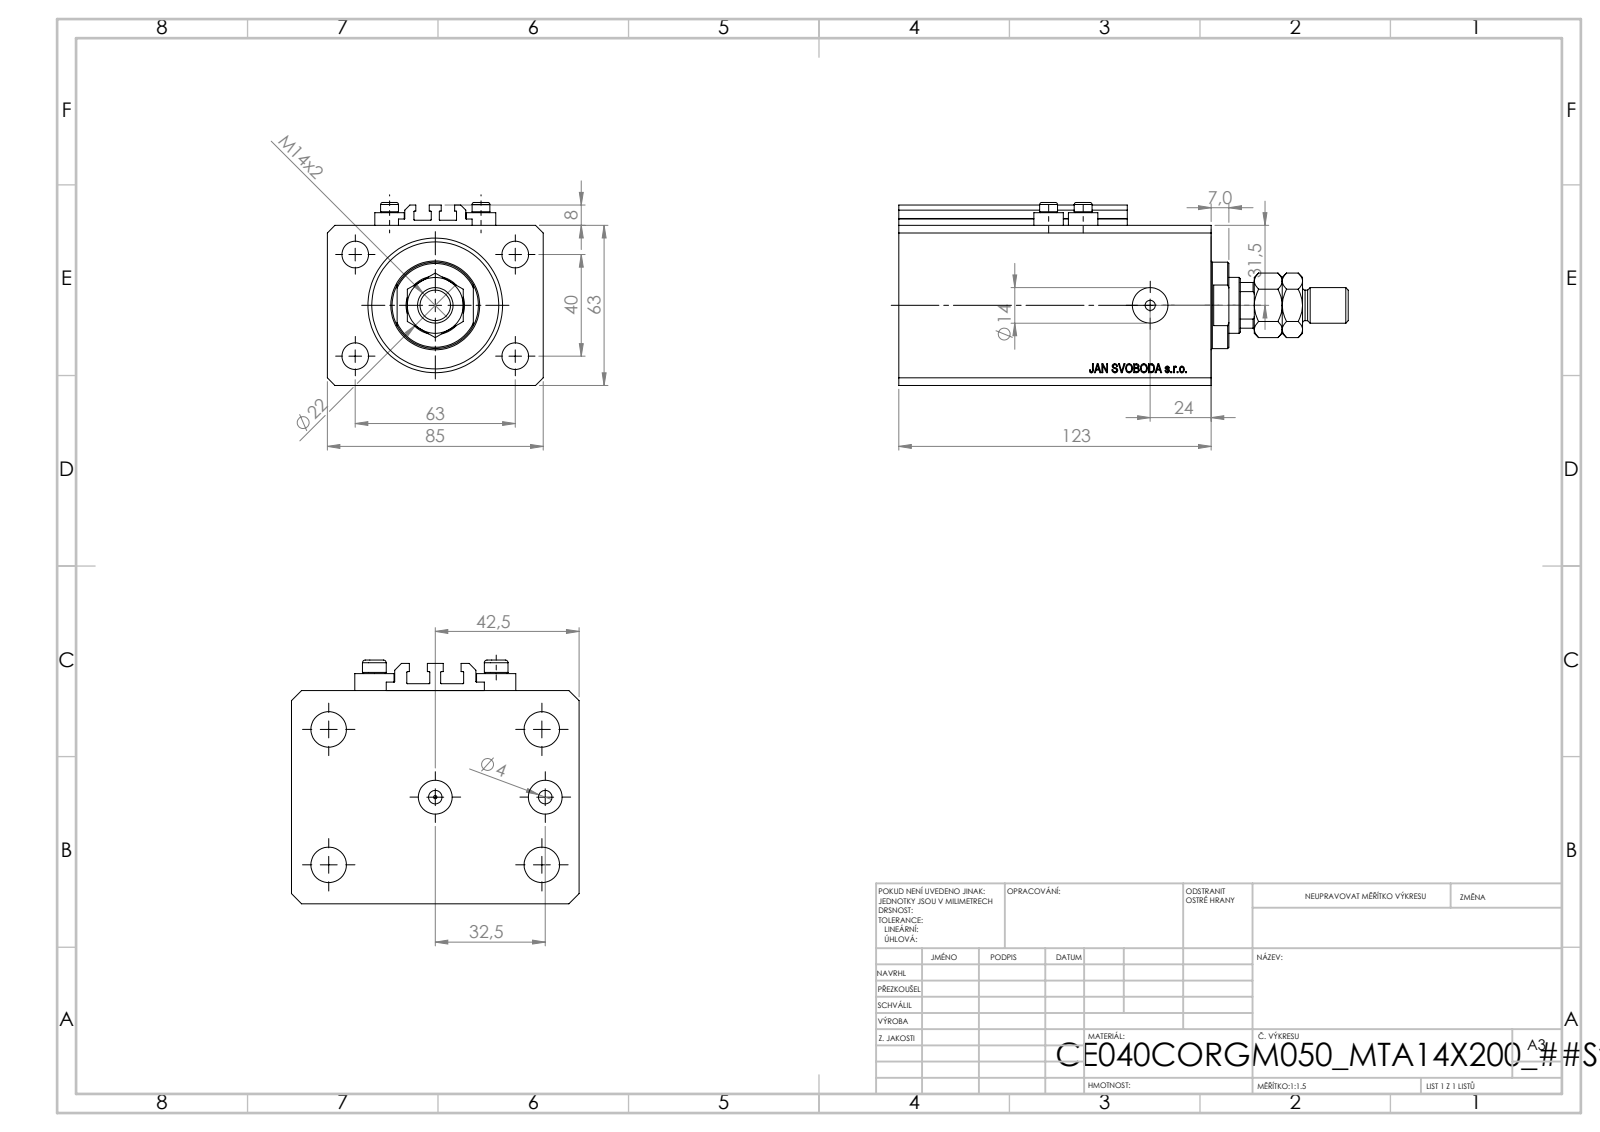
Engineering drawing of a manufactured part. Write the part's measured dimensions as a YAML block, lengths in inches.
part_name: "ALLEN BOLT V250CE; V250CE_C_VCP; V250CE_VC_C; V250CE_C_Body (+1 more)"
step_written_by: "SolidWorks 2019 (CONFIG_CONTROL_DESIGN)"
units: inches
bodies: {solids: 9, faces: 1087, planar: 519, cylindrical: 92, other: 476}
overall_size: [6.969, 3.346, 2.835]
volume: 36.46
surface_area: 181.7
round_holes:
  - {diameter: 0.157, count: 8}
  - {diameter: 0.413, count: 4}
  - {diameter: 0.394, count: 2}
  - {diameter: 0.551, count: 2}
  - {diameter: 0.049, count: 1}
  - {diameter: 0.492, count: 1}
  - {diameter: 0.866, count: 1}
  - {diameter: 1.575, count: 1}
  - {diameter: 2.087, count: 1}
round_bosses_or_shafts:
  - {diameter: 0.457, count: 4}
  - {diameter: 0.276, count: 4}
  - {diameter: 1.339, count: 1}
  - {diameter: 0.551, count: 1}
  - {diameter: 0.472, count: 1}
partial_cylinders:
  - {radius: 0.008, count: 10}
  - {radius: 0.413, count: 1}
face_to_face_distances: [2.48, 3.346, 4.843, 0.669, 4.173, 0.449, 3.724, 4.394, 0.394, 0.098]
hole_center_spacings: [1.469, 0.535, 0.788, 1.417, 1.515, 1.575, 2.48, 2.64]
